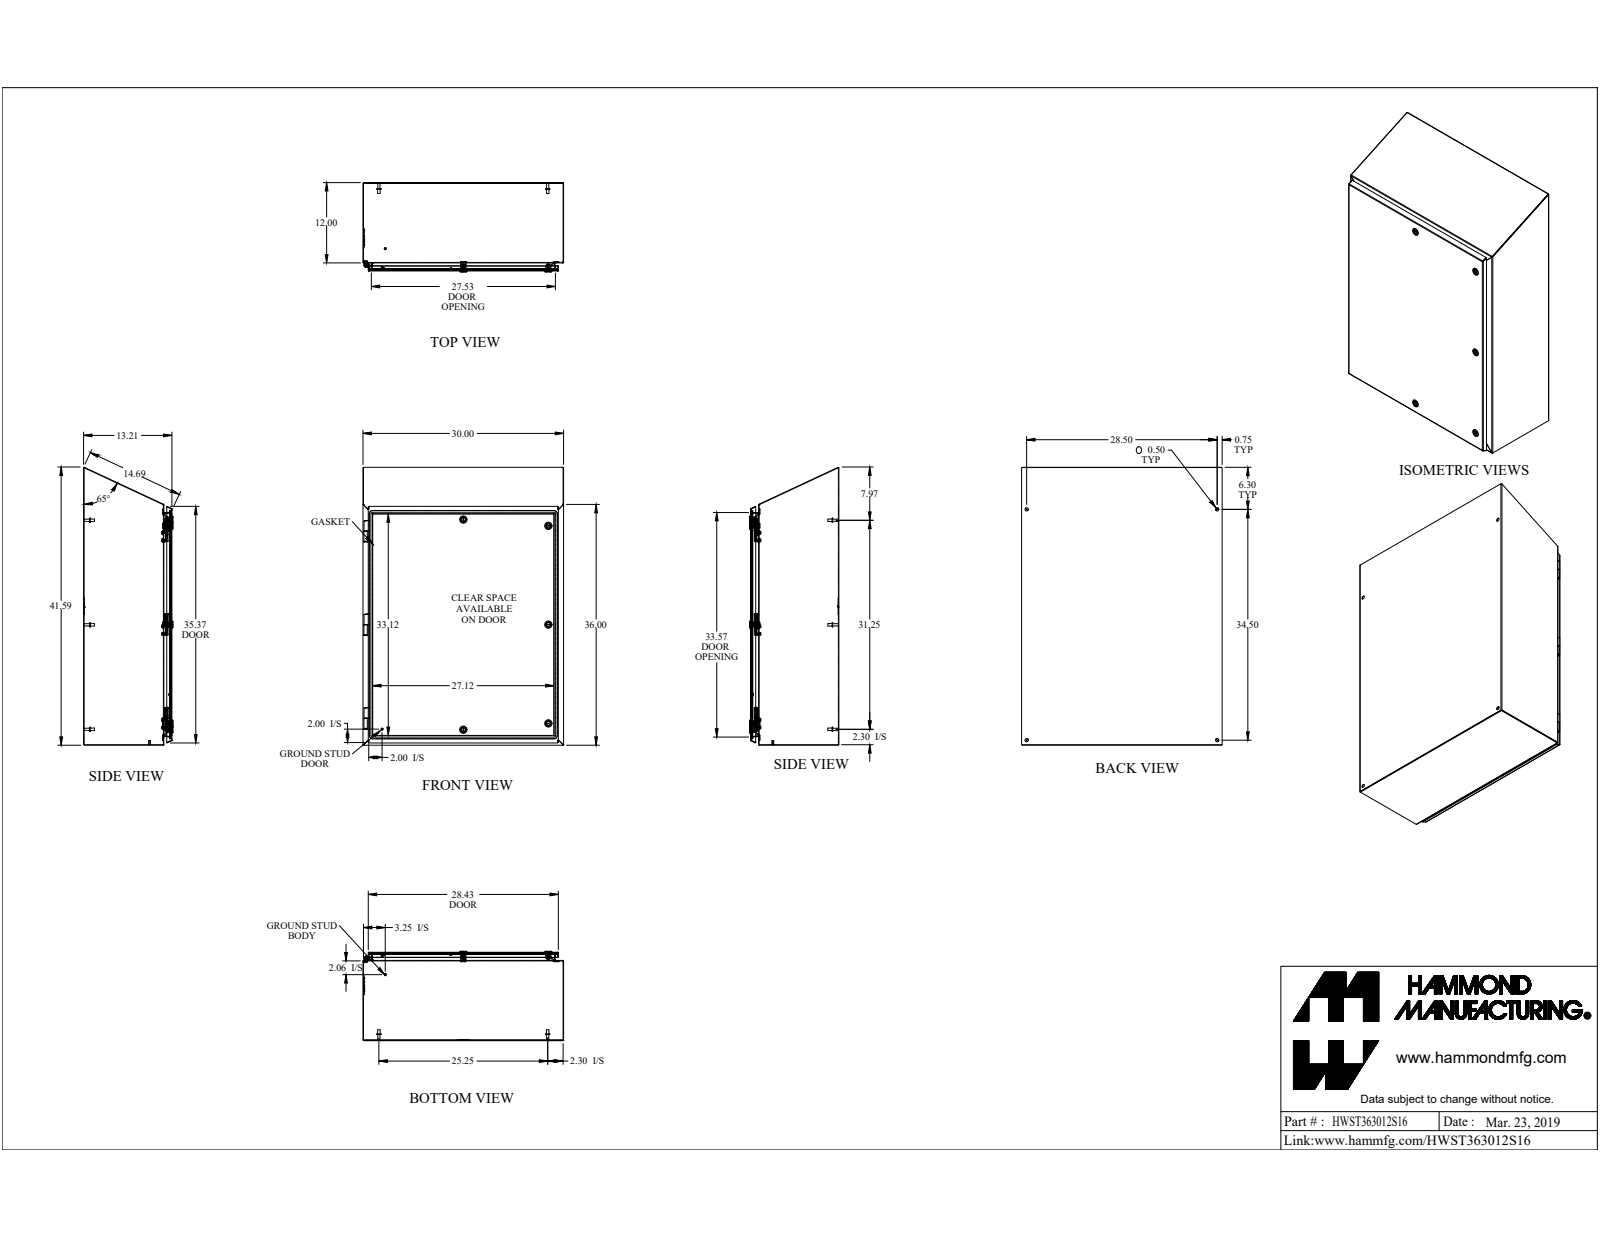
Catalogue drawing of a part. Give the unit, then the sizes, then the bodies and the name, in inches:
Units: inches
Overall size (bounding box): 41.545 × 30 × 13.37
Round holes (diameter × count): ⌀0.194 ×12, ⌀0.24 ×12, ⌀0.5 ×9, ⌀0.275 ×6, ⌀0.197 ×5, ⌀0.387 ×5, ⌀0.63 ×5, ⌀0.768 ×5, ⌀0.13 ×2, ⌀0.24 ×1, ⌀3.5 ×1
Round bosses / shafts (diameter × count): ⌀0.226 ×12, ⌀0.625 ×11, ⌀0.65 ×6, ⌀0.375 ×6, ⌀0.332 ×6, ⌀0.236 ×6, ⌀1.1 ×5, ⌀0.785 ×5
Partial cylindrical surfaces — rounded edges, fillets, slot ends (radius × count): R0.039 ×24, R0.25 ×24, R0.125 ×22, R0.036 ×18, R0.108 ×18, R0.012 ×16, R0.03 ×16, R0.133 ×6
Main face-to-face distances: 0.072, 13.066, 13.138, 0.072, 13.138, 13.21, 29.928, 29.856, 30, 11.928
Hole centre spacings: 1.142, 13.987, 13.987, 27.974, 1.142, 15.129, 12.75, 12.845
Volume: 335.7 in³ · Surface area: 9 162 in²
Bodies: 70 solids, 1632 faces (1011 planar, 430 cylindrical, 191 other)
Part name (STEP PRODUCT): HWST363012S16
STEP written by: SolidWorks 2019 (AUTOMOTIVE_DESIGN)
